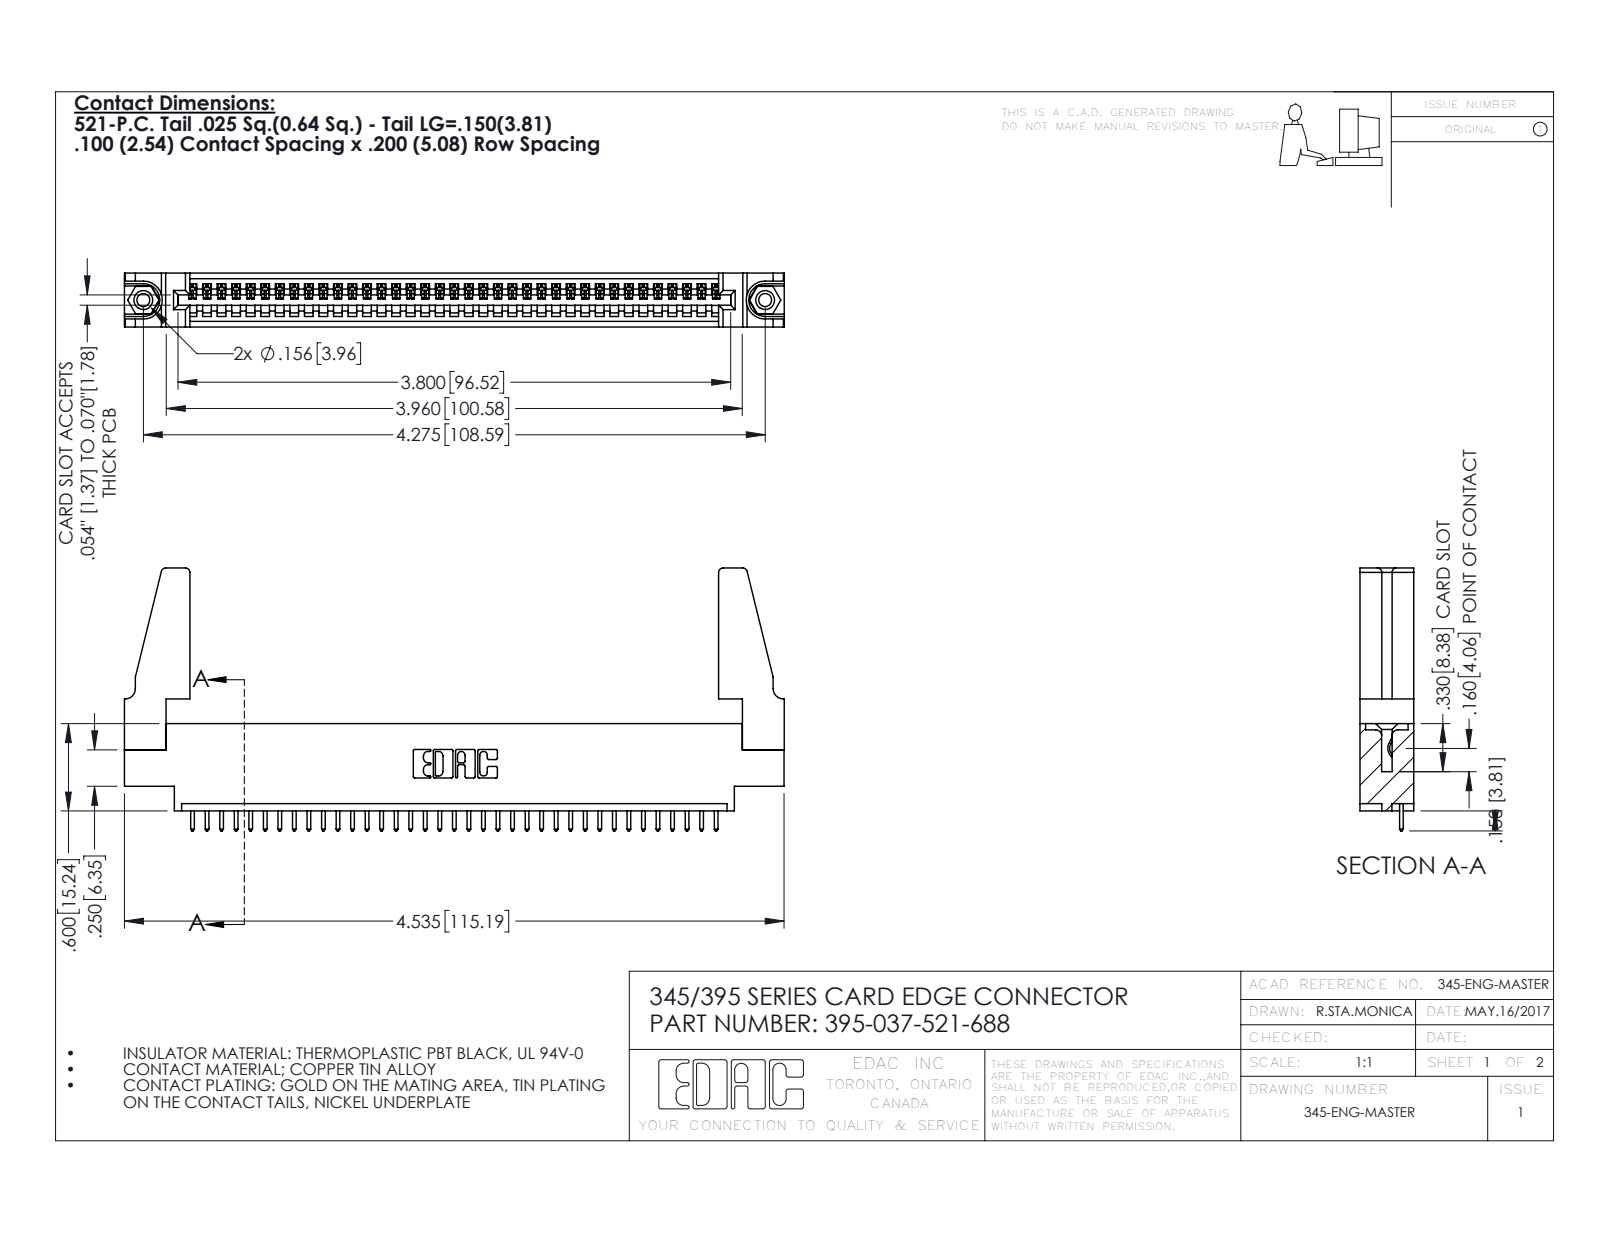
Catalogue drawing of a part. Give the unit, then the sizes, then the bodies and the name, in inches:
Units: inches
Overall size (bounding box): 4.536 × 1.807 × 0.37
Round holes (diameter × count): ⌀0.089 ×2, ⌀0.125 ×2, ⌀0.156 ×2, ⌀0.064 ×1
Round bosses / shafts (diameter × count): ⌀0.155 ×2
Partial cylindrical surfaces — rounded edges, fillets, slot ends (radius × count): R0.006 ×74, R0.01 ×74, R0.01 ×22, R0.03 ×8, R0.007 ×6, R0.031 ×6, R0.026 ×3, R0.031 ×2
Main face-to-face distances: 0.37, 0.072, 0.298, 0.098, 0.272, 0.025, 0.2, 0.225, 0.175, 0.149
Hole centre spacings: 0.27, 4.039, 4.275
Volume: 0.85 in³ · Surface area: 26.31 in²
Bodies: 42 solids, 2400 faces (1636 planar, 748 cylindrical, 16 other)
Part name (STEP PRODUCT): 345-250-001_345-250-001-102; 395-037-521-688; 345 Part_0.170 Offset - 0.156 Dia-TH; 345-220-078_345-220-088 (+1 more)
STEP written by: SolidWorks 2016 (CONFIG_CONTROL_DESIGN)
